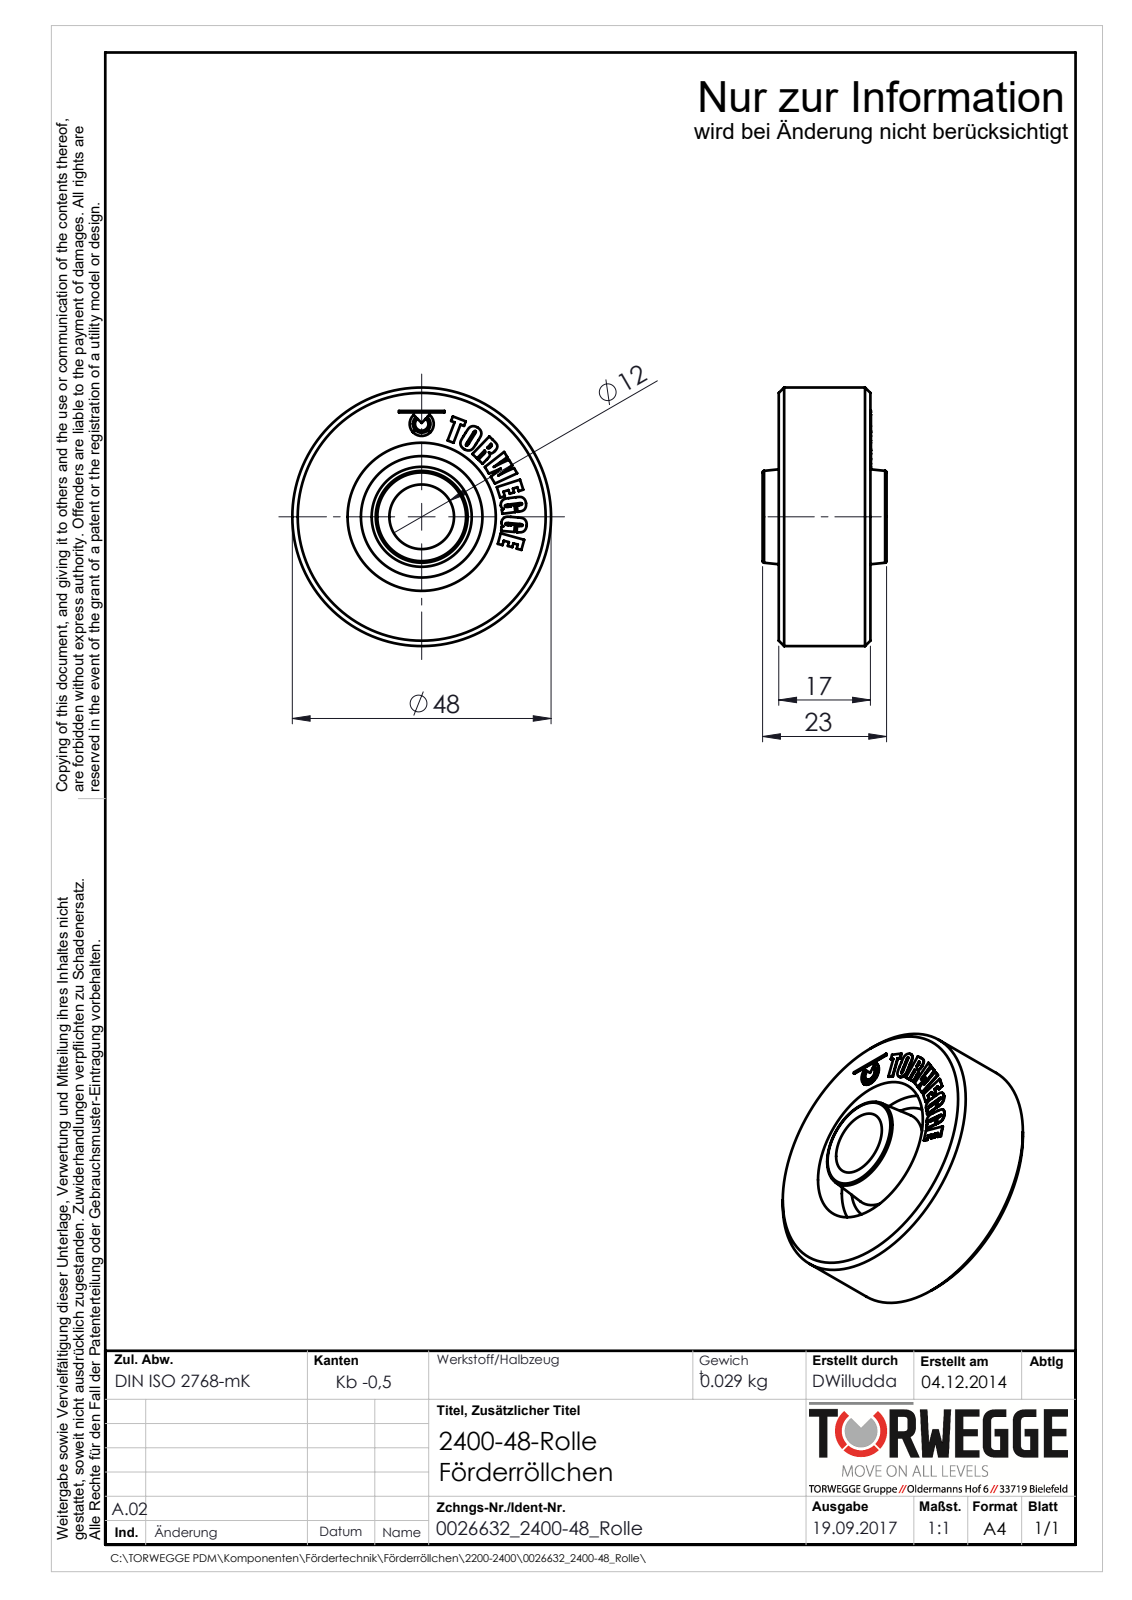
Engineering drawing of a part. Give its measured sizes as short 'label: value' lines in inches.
name: 0026632_2400-48_Rolle
written by: SolidWorks 2016 (AUTOMOTIVE_DESIGN)
unit: in
bodies: 2 solids, 198 faces (117 planar, 20 cylindrical, 61 other)
size: 1.89 × 1.89 × 0.906
volume: 1.549 in³; area: 24.01 in²
holes: 1× ⌀0.472, 1× ⌀1.083, 1× ⌀1.201, 1× ⌀1.496
bosses: 1× ⌀1.89
face distances: 0.079, 0.591, 0.669, 0.246, 0.423, 0.167, 0.344, 0.512, 0.177, 0.118
